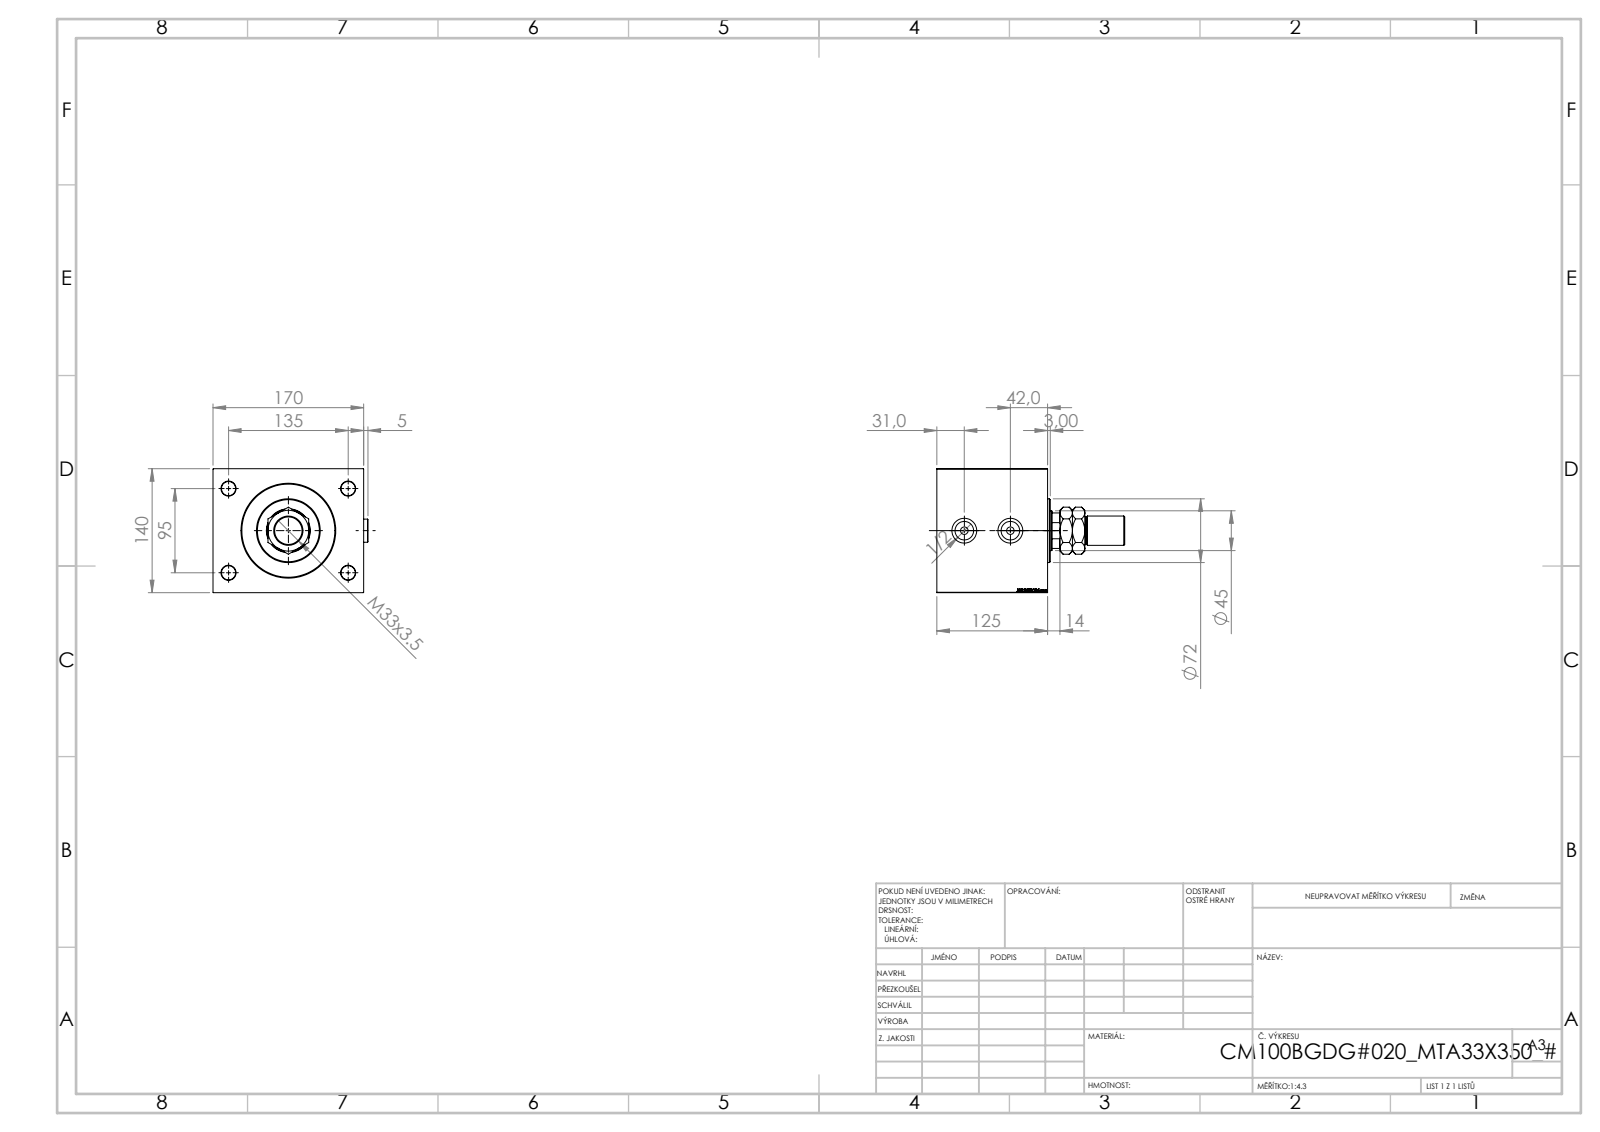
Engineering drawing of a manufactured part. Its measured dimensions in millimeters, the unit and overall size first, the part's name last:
Units: millimetres
Overall size (bounding box): 212 × 174.9 × 140
Round holes (diameter × count): ⌀16 ×4, ⌀8.5 ×2, ⌀20.96 ×2, ⌀28 ×2, ⌀31.5 ×1, ⌀45 ×1, ⌀48.5 ×1, ⌀49.5 ×1, ⌀100 ×1, ⌀102 ×1, ⌀105 ×1
Round bosses / shafts (diameter × count): ⌀26 ×2, ⌀72 ×1, ⌀33 ×1, ⌀31 ×1
Partial cylindrical surfaces — rounded edges, fillets, slot ends (radius × count): R22 ×1
Main face-to-face distances: 140, 125, 170, 51, 74, 21.6, 29.4, 103.4, 10, 31.6
Hole centre spacings: 82.54, 95, 135, 165.08, 52
Volume: 2 922 000 mm³ · Surface area: 234 354 mm²
Bodies: 6 solids, 985 faces (451 planar, 74 cylindrical, 460 other)
Part name (STEP PRODUCT): MTA; V450CM_B_Body; V450CM_VC_B; Zatka_OIL_PORT (+1 more)
STEP written by: SolidWorks 2019 (CONFIG_CONTROL_DESIGN)
